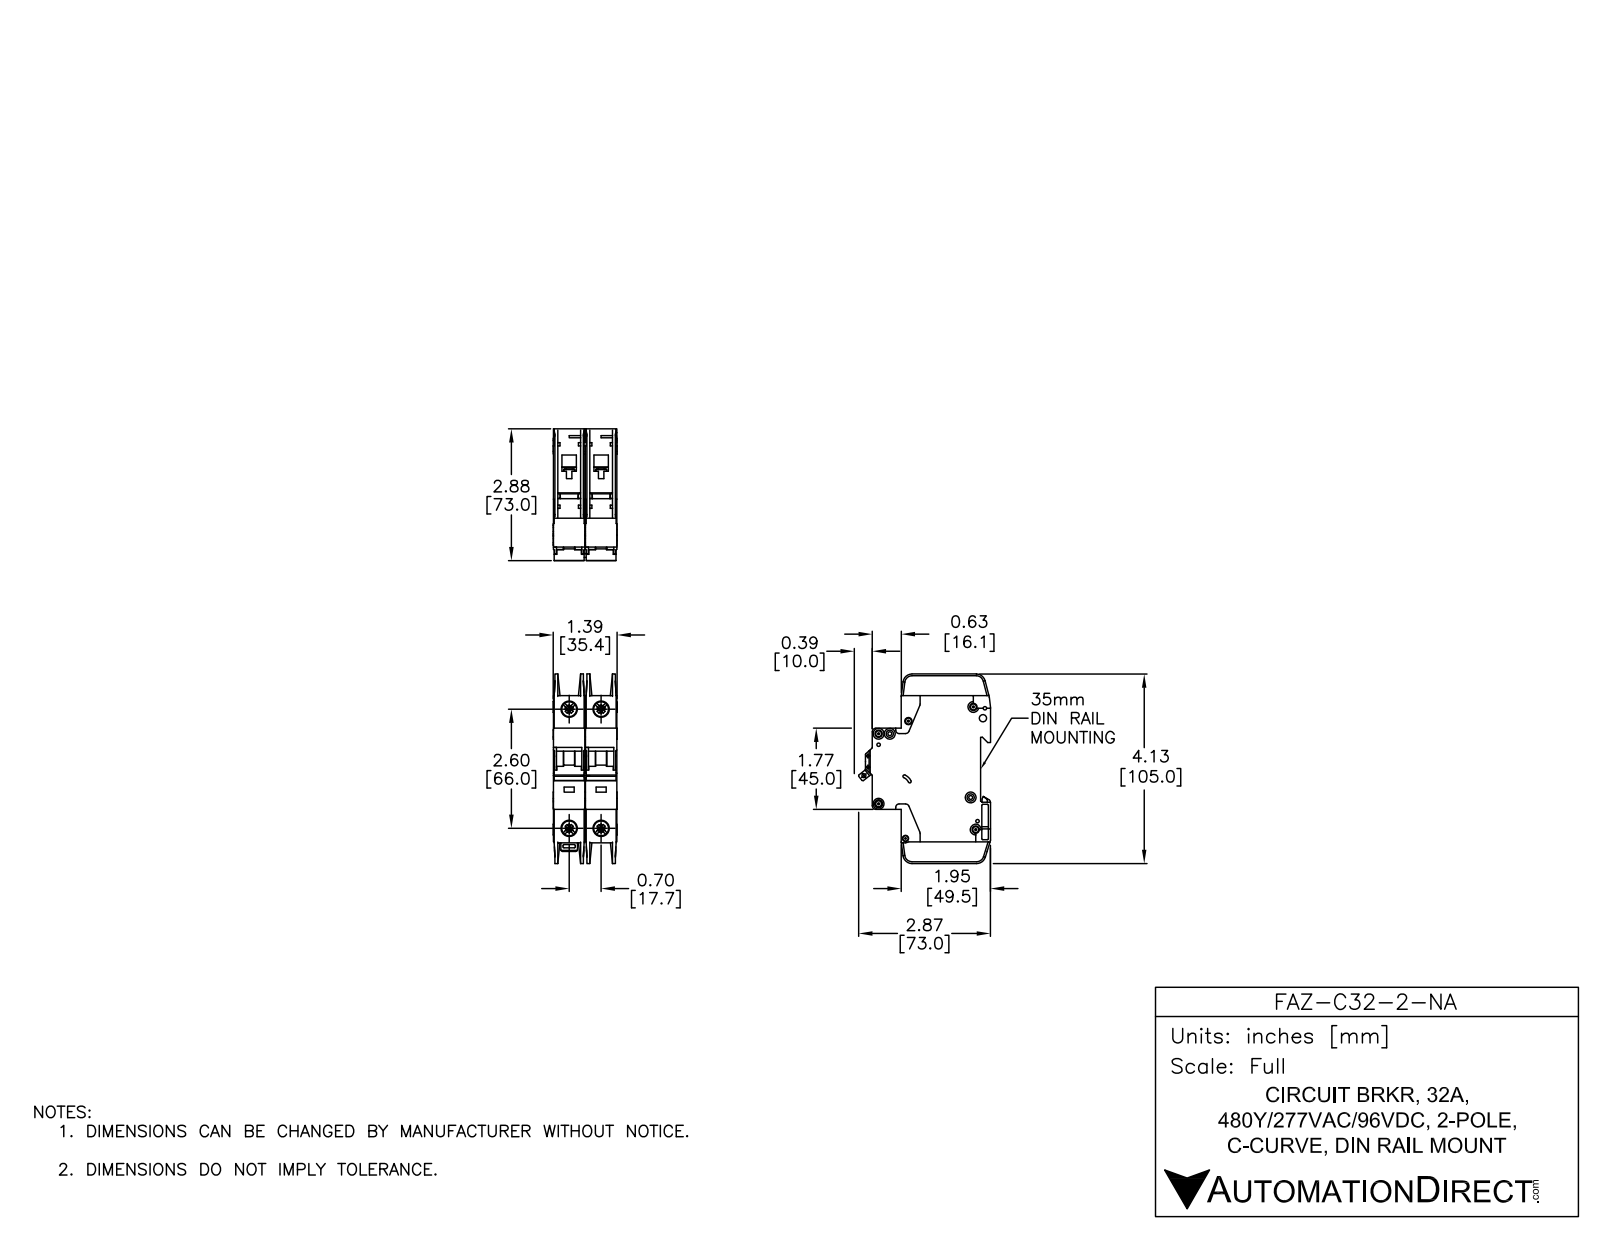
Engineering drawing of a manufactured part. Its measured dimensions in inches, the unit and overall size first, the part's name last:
Units: inches
Overall size (bounding box): 4.134 × 2.876 × 1.394
Round holes (diameter × count): ⌀0.142 ×7, ⌀0.281 ×4, ⌀0.323 ×4, ⌀0.043 ×2, ⌀0.059 ×2, ⌀0.157 ×2, ⌀0.075 ×1, ⌀0.085 ×1, ⌀0.087 ×1, ⌀0.1 ×1, ⌀0.13 ×1, ⌀0.134 ×1
Round bosses / shafts (diameter × count): ⌀0.236 ×7, ⌀0.098 ×2
Partial cylindrical surfaces — rounded edges, fillets, slot ends (radius × count): R0.01 ×47, R0.02 ×24, R0.039 ×18, R0.079 ×12, R0.197 ×5, R0.071 ×4, R0.157 ×4, R0.008 ×2
Main face-to-face distances: 0.697, 0.689, 0.028, 0.593, 0.096, 0.069, 0.62, 0.524, 1.386, 0.669
Hole centre spacings: 0.244, 0.697, 2.598, 2.69, 0.204, 0.24, 0.322, 0.337
Volume: 9.482 in³ · Surface area: 76.69 in²
Bodies: 6 solids, 1568 faces (818 planar, 526 cylindrical, 224 other)
Part name (STEP PRODUCT): FAZ-C32-2-NA
STEP written by: SolidWorks 2014 (AUTOMOTIVE_DESIGN)
